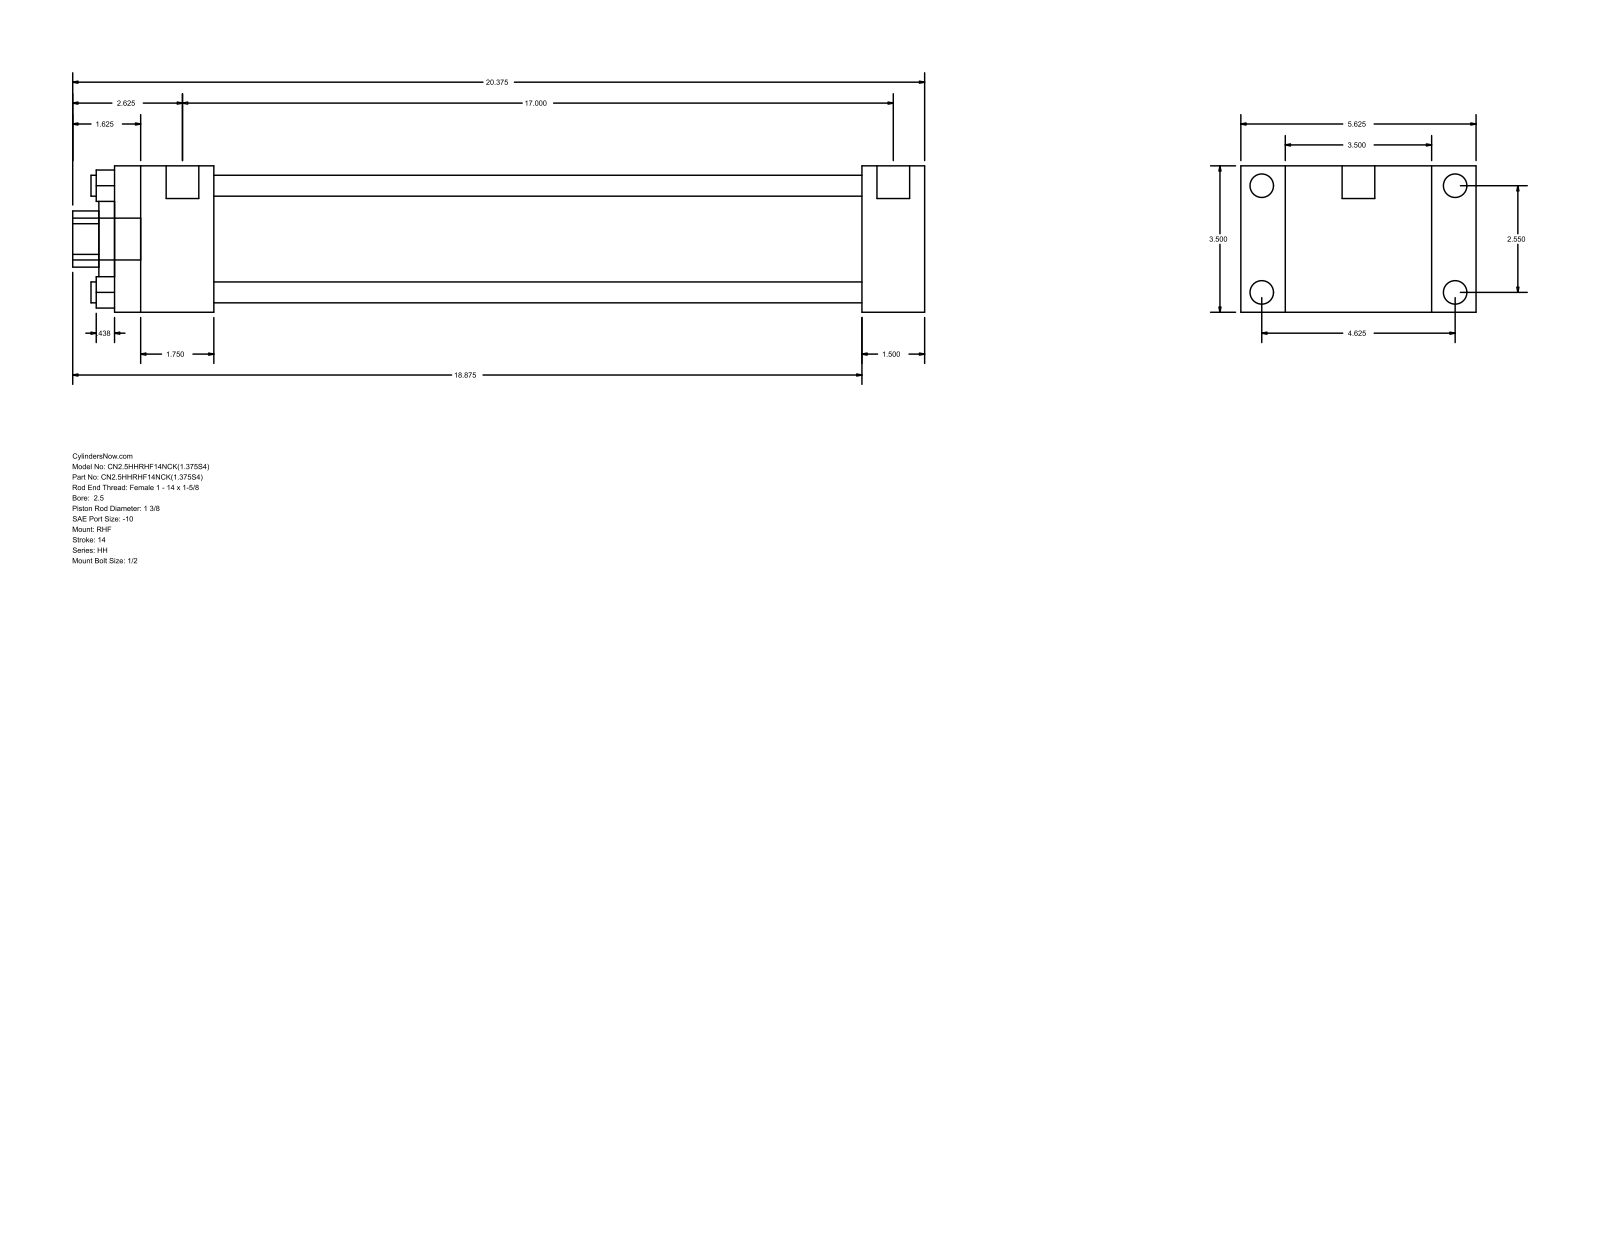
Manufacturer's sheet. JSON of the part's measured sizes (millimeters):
{"part_name": "HH_RHF__0250_1.375", "step_written_by": "GSSL Pune (CONFIG_CONTROL_DESIGN)", "units": "millimeters", "bodies": {"solids": 0, "faces": 88, "planar": 60, "cylindrical": 28, "other": 0}, "overall_size": [517.52, 142.88, 88.9], "round_holes": [[12.7, 4], [34.92, 1], [50.8, 1], [73.03, 1]], "round_bosses_or_shafts": [[14.3, 4], [5.56, 4], [19.84, 2], [25.4, 1]], "partial_cylinders_radius": [[17.06, 1]], "face_to_face_distances": [88.9, 38.09, 26.99, 115.89, 454.03, 492.12, 142.88, 60.32, 393.71, 431.8], "hole_center_spacings": [45.79, 64.76, 91.58]}
